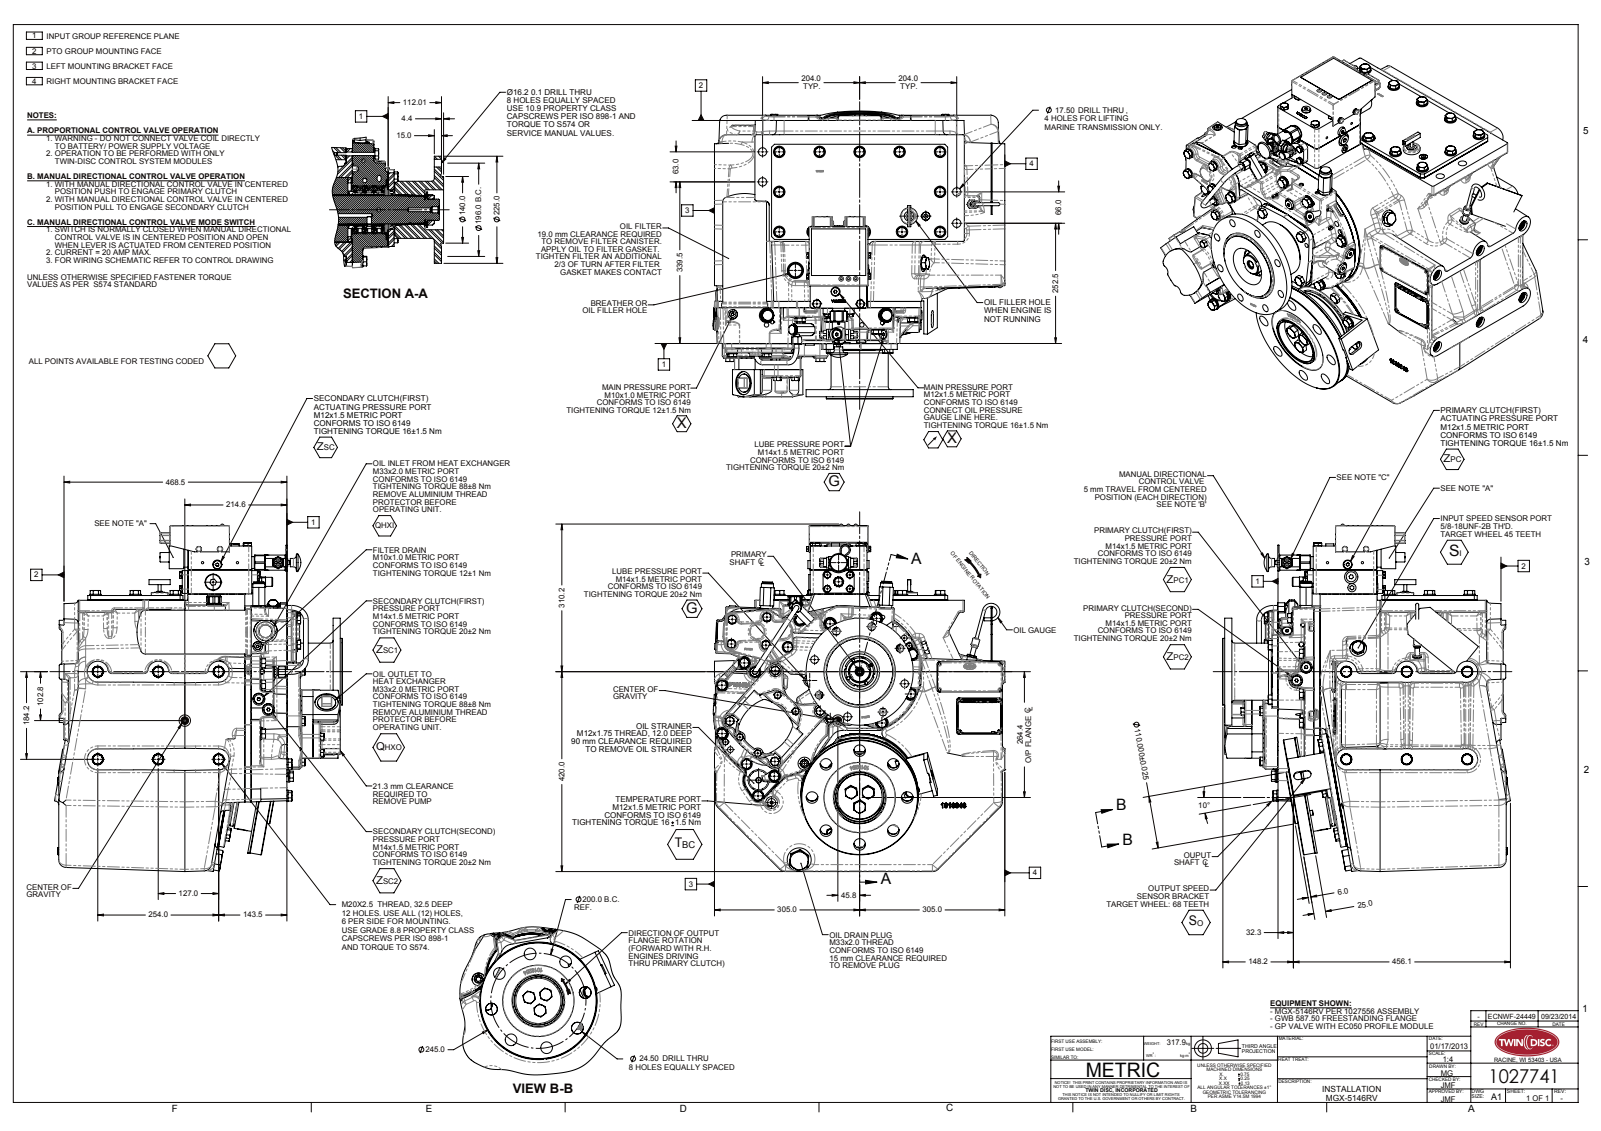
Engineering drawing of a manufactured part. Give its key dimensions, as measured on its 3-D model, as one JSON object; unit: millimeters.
{"part_name": "1027741", "step_written_by": "SolidWorks 2010 (AUTOMOTIVE_DESIGN)", "units": "millimeters", "bodies": {"solids": 0, "faces": 5065, "planar": 1906, "cylindrical": 1385, "other": 1774}, "overall_size": [855.94, 653.44, 611.05], "round_holes": [[12, 16], [25, 11], [16.2, 8], [24.5, 8], [23.51, 6], [20, 5], [6.35, 4], [10, 4], [17.5, 4], [4.76, 3], [7.71, 3], [9.33, 3]], "round_bosses_or_shafts": [[24, 26], [19, 8], [19.85, 5], [14, 5], [10, 5], [2.54, 5], [17, 4], [13, 4]], "partial_cylinders_radius": [[3, 103], [8, 74], [6.5, 62], [2.5, 55], [16, 32], [6, 25], [3.05, 21], [1.02, 16]], "face_to_face_distances": [0.39, 13.09, 404.48, 404.09, 13.48, 391, 10.06, 75, 75.39, 88.48], "hole_center_spacings": [100, 76.54, 141.42, 184.78, 127, 82, 184.77, 200]}
